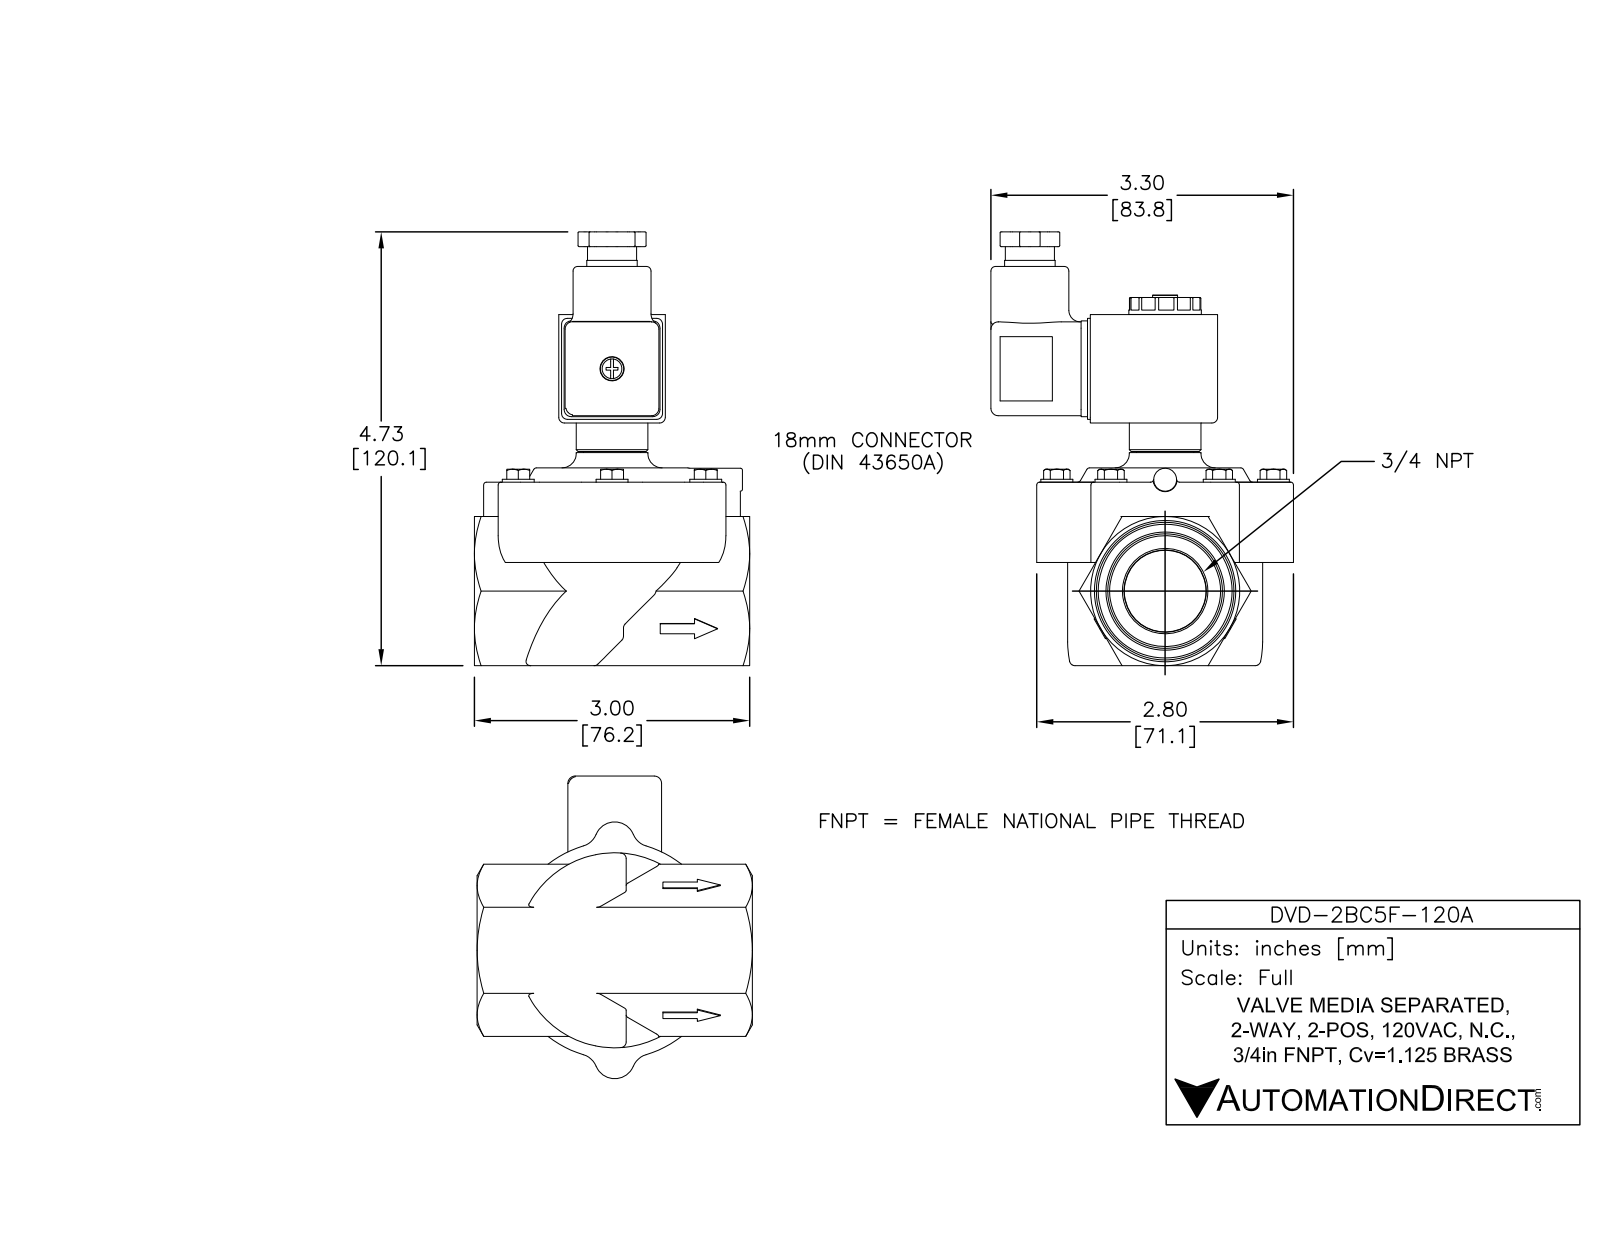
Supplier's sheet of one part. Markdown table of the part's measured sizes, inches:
| quantity | value |
| --- | --- |
| part name | DVD-2BC5F-120A |
| STEP written by | SolidWorks 2015 (AUTOMOTIVE_DESIGN) |
| units | inches |
| bodies | 4 solids, 1888 faces (891 planar, 379 cylindrical, 618 other) |
| overall size | 4.727 × 3.298 × 3 |
| volume | 9.098 in³ |
| surface area | 104.5 in² |
| round holes (diameter × count) | 0.2 × 6, 0.236 × 6, 0.185 × 4, 0.06 × 2, 0.062 × 2, 0.125 × 2, 0.156 × 2, 0.185 × 2, 0.047 × 1, 0.065 × 1, 0.078 × 1, 0.089 × 1 |
| round bosses / shafts (diameter × count) | 0.348 × 6, 0.234 × 6, 0.164 × 6, 1.844 × 1, 1.5 × 1, 1.359 × 1, 0.85 × 1, 0.79 × 1 |
| partial cylindrical surfaces (radius × count) | 0.01 × 48, 0.219 × 20, 0.062 × 12, 0.08 × 12, 0.156 × 12, 0.03 × 10, 0.05 × 8, 0.031 × 7 |
| main face-to-face distances | 1.615, 1.635, 0.125, 0.02, 0.92, 2.08, 1.625, 0.155, 0.25, 0.048 |
| hole center spacings | 1.18, 1.18, 2.044, 0.611, 1.669, 2.28, 1.103, 1.169 |
